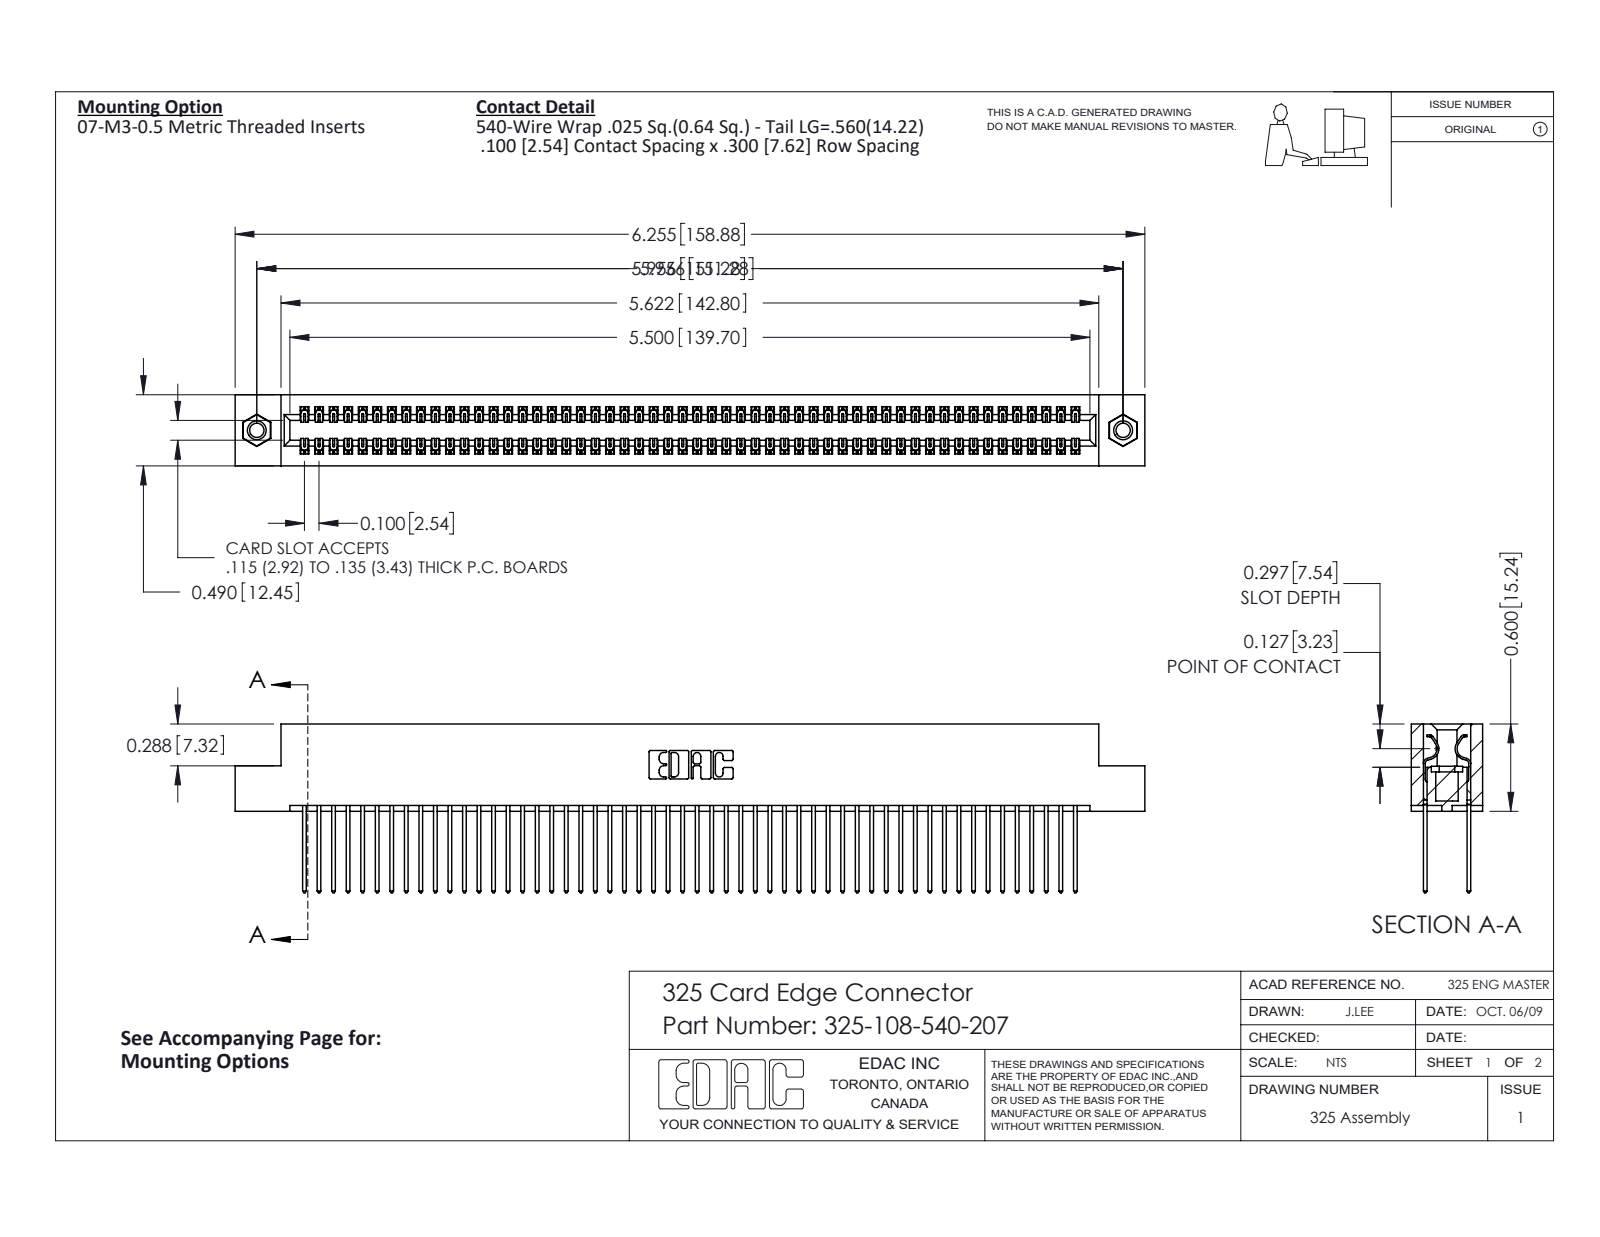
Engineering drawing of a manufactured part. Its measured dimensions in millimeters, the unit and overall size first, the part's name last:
Units: millimetres
Overall size (bounding box): 158.9 × 29.5 × 12.4
Round holes (diameter × count): ⌀2.5 ×2, ⌀3.2 ×2, ⌀4.1 ×2
Round bosses / shafts (diameter × count): ⌀3.9 ×2
Partial cylindrical surfaces — rounded edges, fillets, slot ends (radius × count): R0.2 ×162, R0.3 ×108, R0.3 ×22, R0.2 ×6, R0.8 ×6, R0.7 ×3, R0.4 ×2, R0.6 ×2
Main face-to-face distances: 2.1, 10.3, 7.6, 2.7, 9.7, 0.6, 8.3, 12.4, 7, 14.2
Hole centre spacings: 151.3
Volume: 21 010 mm³ · Surface area: 27 700 mm²
Bodies: 111 solids, 5790 faces (3990 planar, 1784 cylindrical, 16 other)
Part name (STEP PRODUCT): 325 Part_TI; 325-292-001_325-293-140; 325-108-540-207; 345-250-001_345-250-005-103
STEP written by: SolidWorks 2016 (CONFIG_CONTROL_DESIGN)
